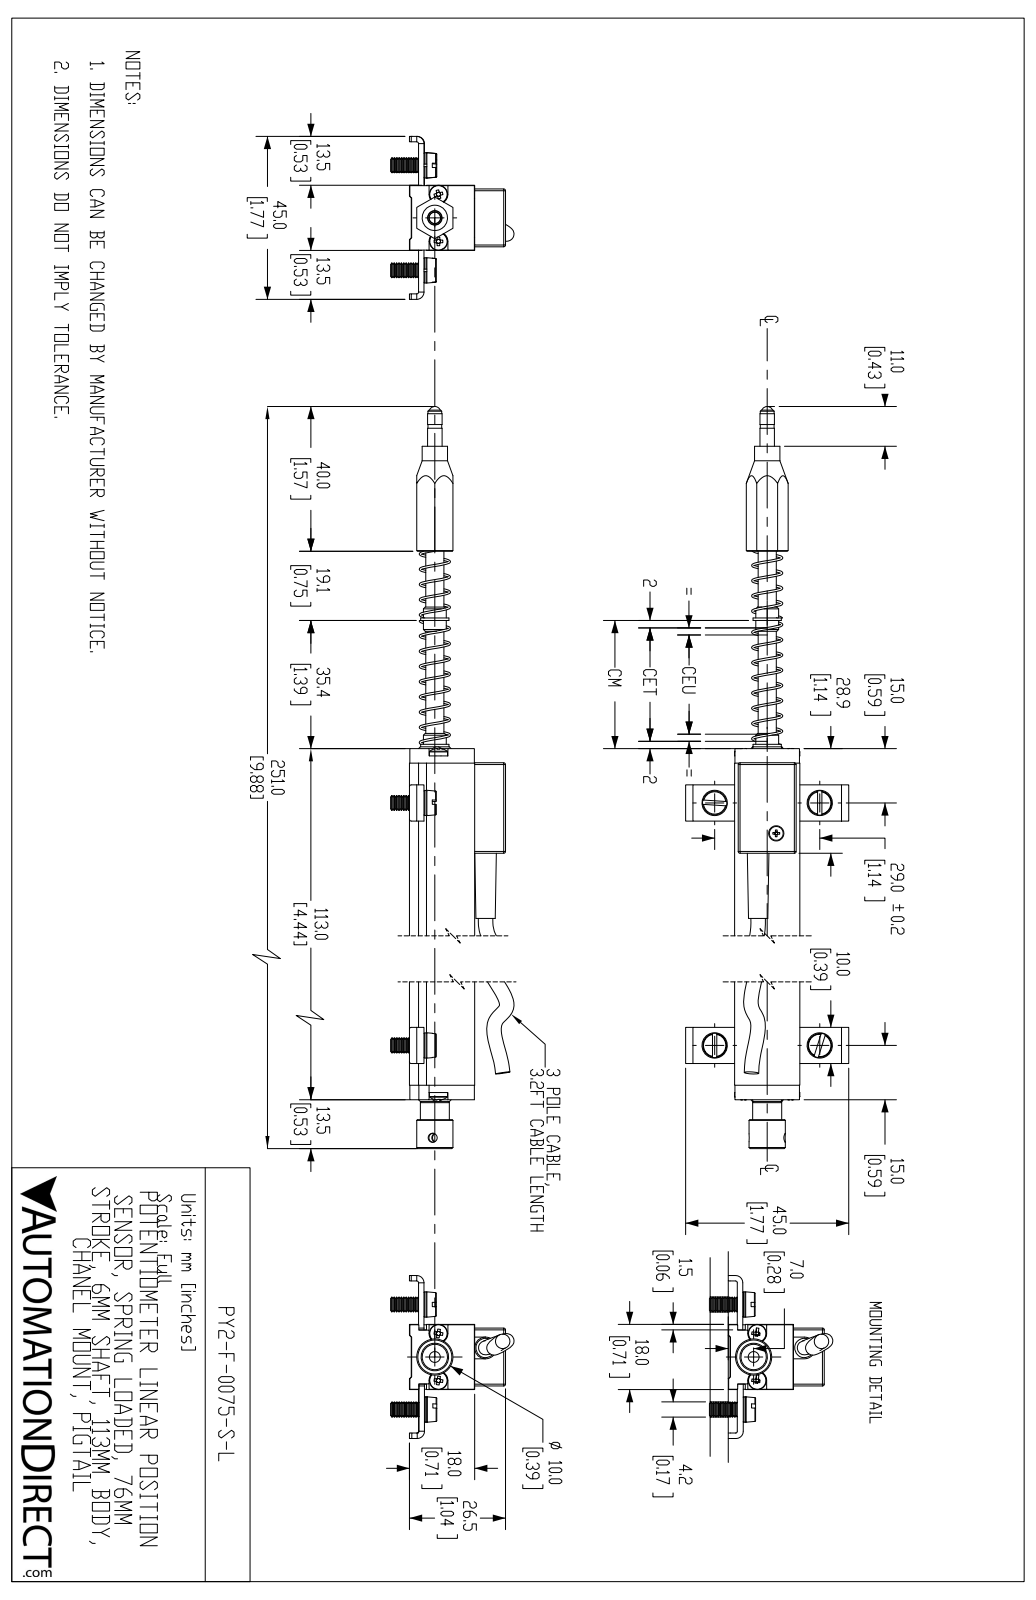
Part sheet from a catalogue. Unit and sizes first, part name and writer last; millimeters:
Units: millimetres
Overall size (bounding box): 250.5 × 45 × 34
Round holes (diameter × count): ⌀3.6 ×4, ⌀4.3 ×4, ⌀2.3 ×2, ⌀2.5 ×2, ⌀2.7 ×2, ⌀6 ×2, ⌀1.6 ×1, ⌀2 ×1, ⌀2.1 ×1, ⌀2.6 ×1, ⌀4 ×1, ⌀4.2 ×1
Round bosses / shafts (diameter × count): ⌀4 ×6, ⌀7 ×4, ⌀5 ×3, ⌀2.5 ×3, ⌀3.8 ×2, ⌀10 ×1, ⌀8 ×1, ⌀7.8 ×1
Partial cylindrical surfaces — rounded edges, fillets, slot ends (radius × count): R0.5 ×25, R2 ×4, R2.6 ×2, R4.5 ×1
Main face-to-face distances: 18, 1.5, 0.5, 2, 17.5, 15.5, 4, 2.5, 16.5, 1
Hole centre spacings: 6.6, 14.6, 29, 83, 85.8, 87.9, 10.3, 13
Volume: 46 360 mm³ · Surface area: 27 580 mm²
Bodies: 35 solids, 990 faces (335 planar, 253 cylindrical, 402 other)
Part name (STEP PRODUCT): PY2-F-0075-S-L
STEP written by: SolidWorks 2019 (AUTOMOTIVE_DESIGN)
